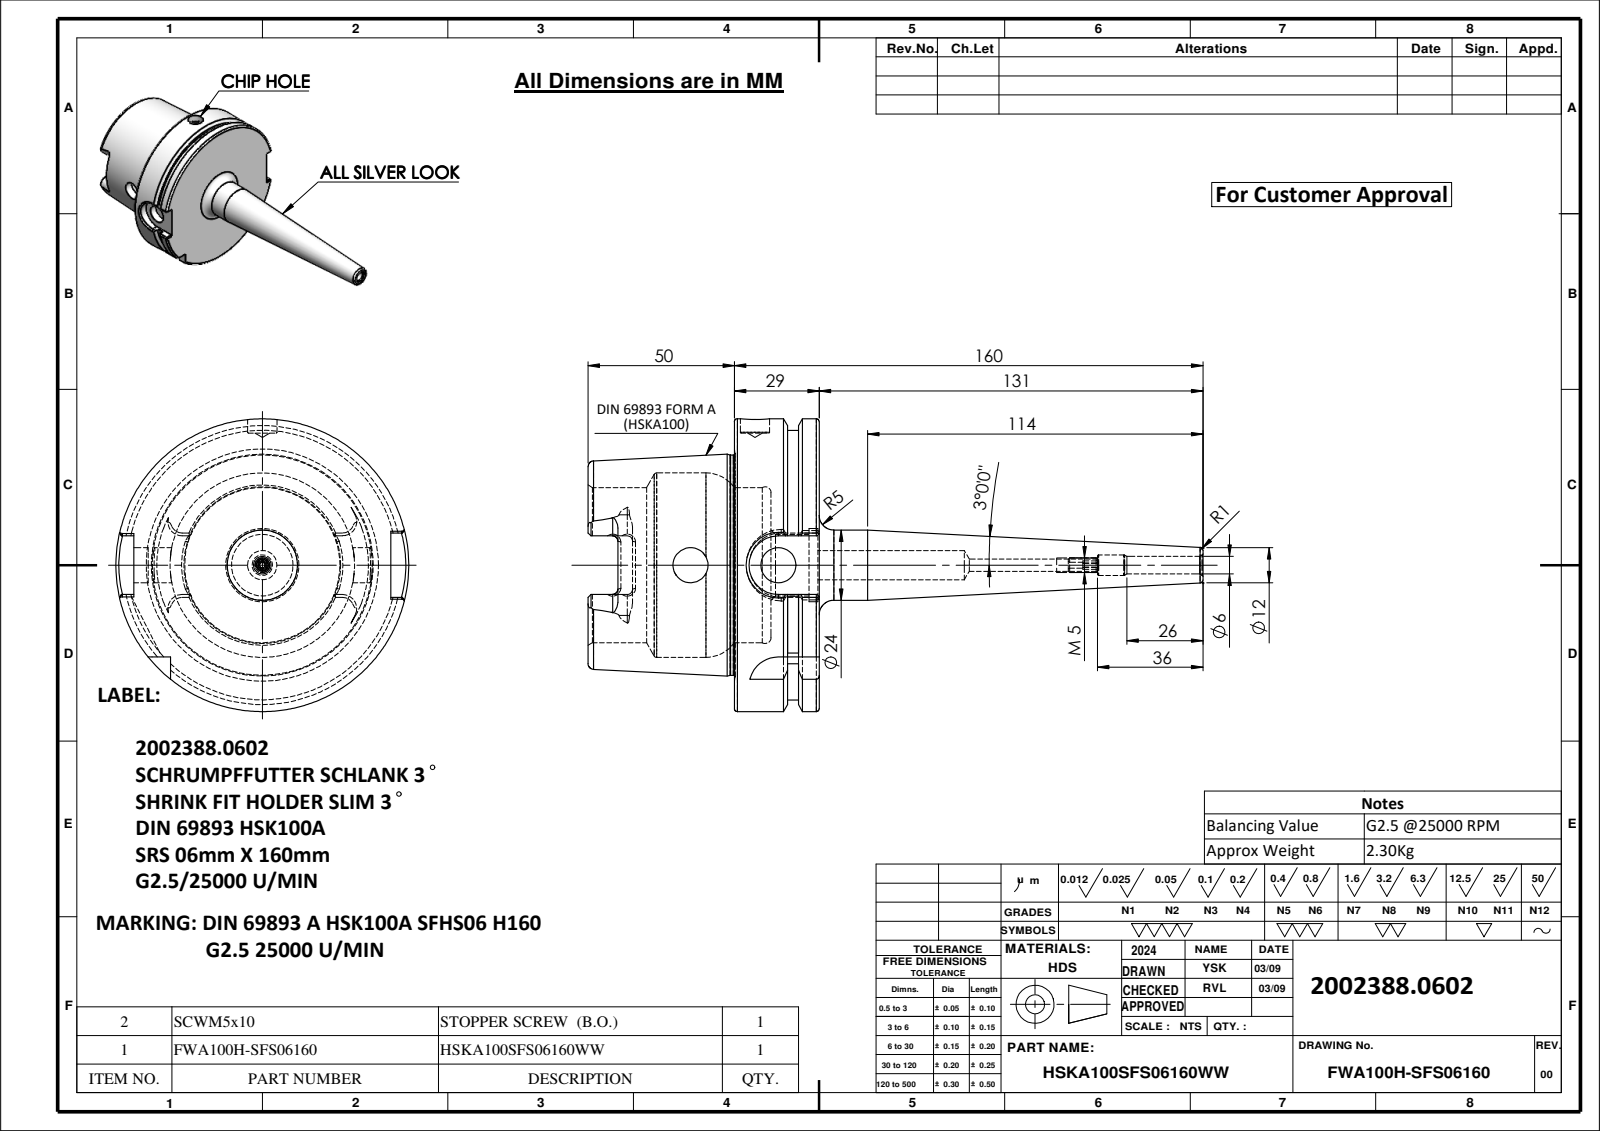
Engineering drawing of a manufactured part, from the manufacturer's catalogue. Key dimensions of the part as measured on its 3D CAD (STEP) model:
Part name (STEP PRODUCT): FWA100H-SFS06160; HSKA100SFS06160WW; SCWM5X10
STEP written by: SolidWorks 2024 (CONFIG_CONTROL_DESIGN)
Units: millimetres
Bodies: 2 solids, 211 faces (67 planar, 58 cylindrical, 86 other)
Overall size (bounding box): 210 × 100 × 100
Volume: 286 220 mm³ · Surface area: 60 214 mm²
Round holes (diameter × count): ⌀10 ×2, ⌀12 ×2, ⌀2 ×1, ⌀4.2 ×1, ⌀6 ×1, ⌀7 ×1, ⌀21 ×1, ⌀25 ×1, ⌀53 ×1, ⌀63 ×1
Round bosses / shafts (diameter × count): ⌀100 ×1, ⌀92 ×1, ⌀75.16 ×1, ⌀24 ×1, ⌀5 ×1
Partial cylindrical surfaces — rounded edges, fillets, slot ends (radius × count): R1.8 ×6, R4.88 ×4, R10 ×2, R11 ×1
Main face-to-face distances: 28.95, 12.5, 16.45, 50, 62.5, 78.95, 78.5, 28.5, 16, 0.45
Hole centre spacings: 30
